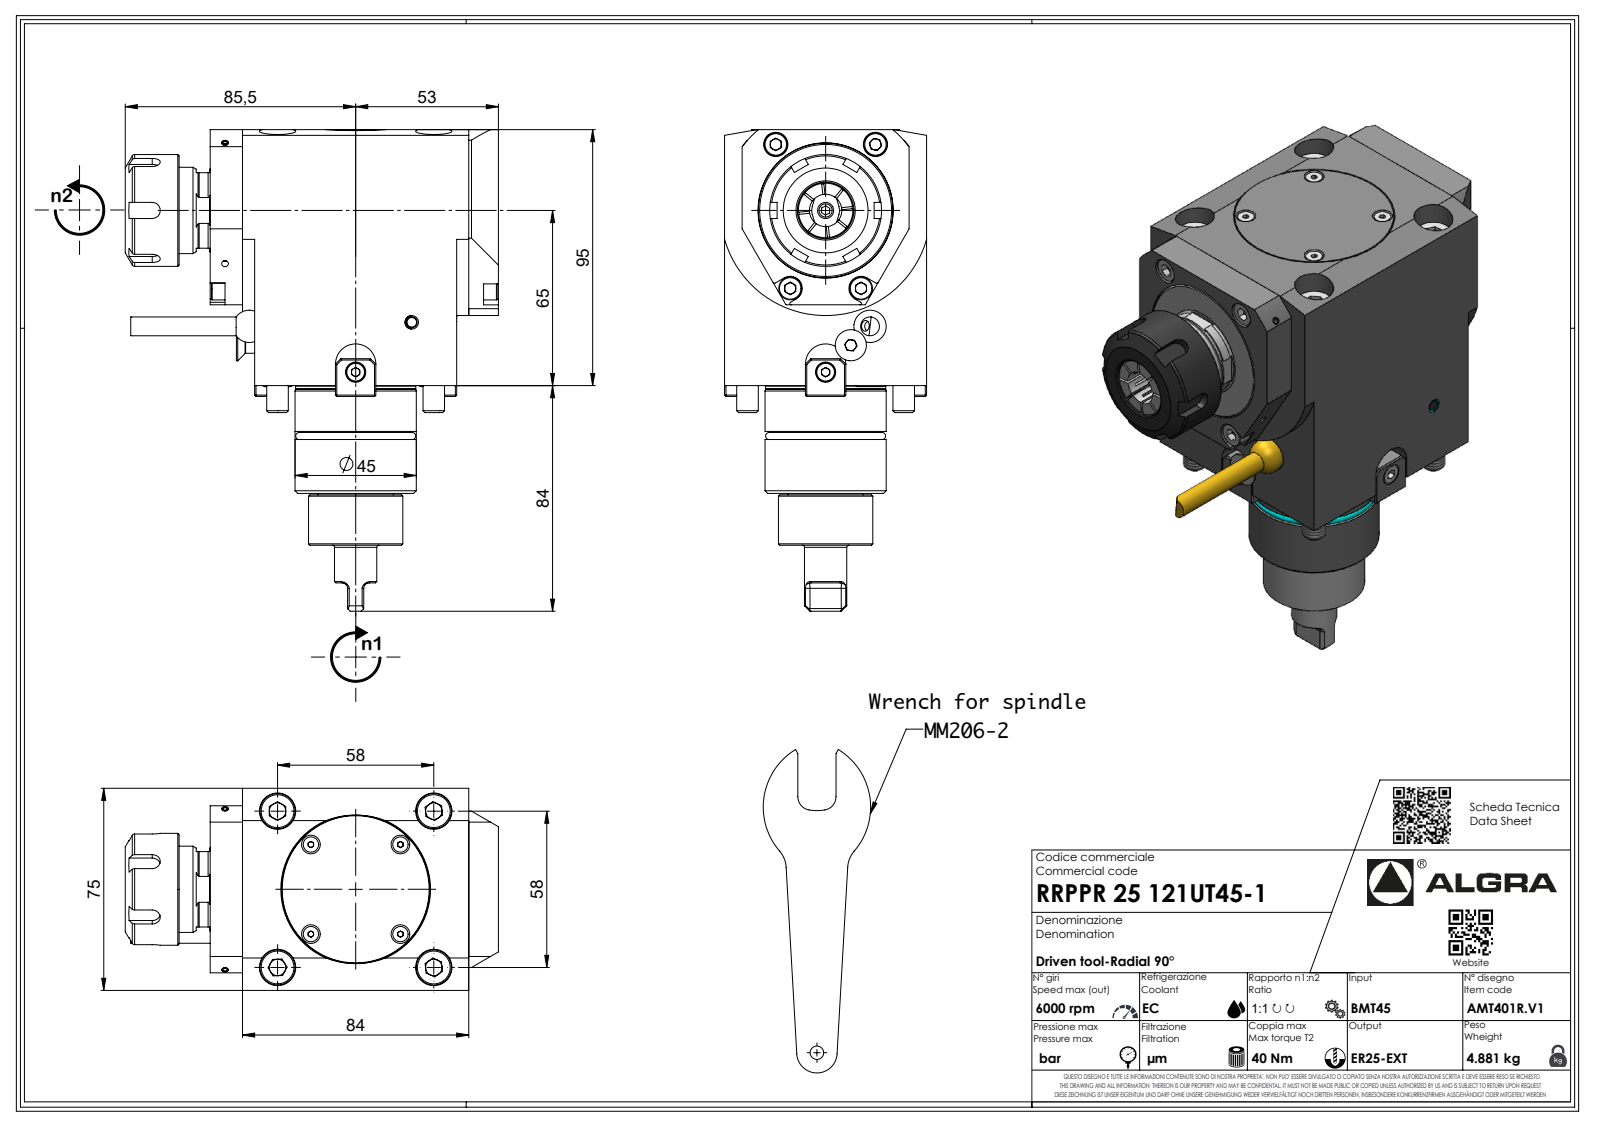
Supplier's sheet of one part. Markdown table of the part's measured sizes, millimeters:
| quantity | value |
| --- | --- |
| part name | RRPPR25121UT45-1 |
| STEP written by | SolidWorks 2023 (AUTOMOTIVE_DESIGN) |
| units | millimeters |
| bodies | 1 solid, 637 faces (447 planar, 86 cylindrical, 104 other) |
| overall size | 178.7 × 138.38 × 75 |
| volume | 759 630 mm³ |
| surface area | 63 100 mm² |
| round holes (diameter × count) | 2.1 × 1, 54 × 1 |
| round bosses / shafts (diameter × count) | 45 × 1, 44.6 × 1, 41.5 × 1, 40.2 × 1, 35 × 1, 32 × 1, 28 × 1, 15.7 × 1 |
| partial cylindrical surfaces (radius × count) | 0.33 × 7, 0.52 × 7, 3.7 × 7, 2 × 6, 3 × 5, 0.5 × 4, 4.5 × 4, 7.5 × 2 |
| main face-to-face distances | 75, 95, 15.5, 90.5, 16.35, 91.35, 106.85, 4.5, 79.5, 95.85 |
